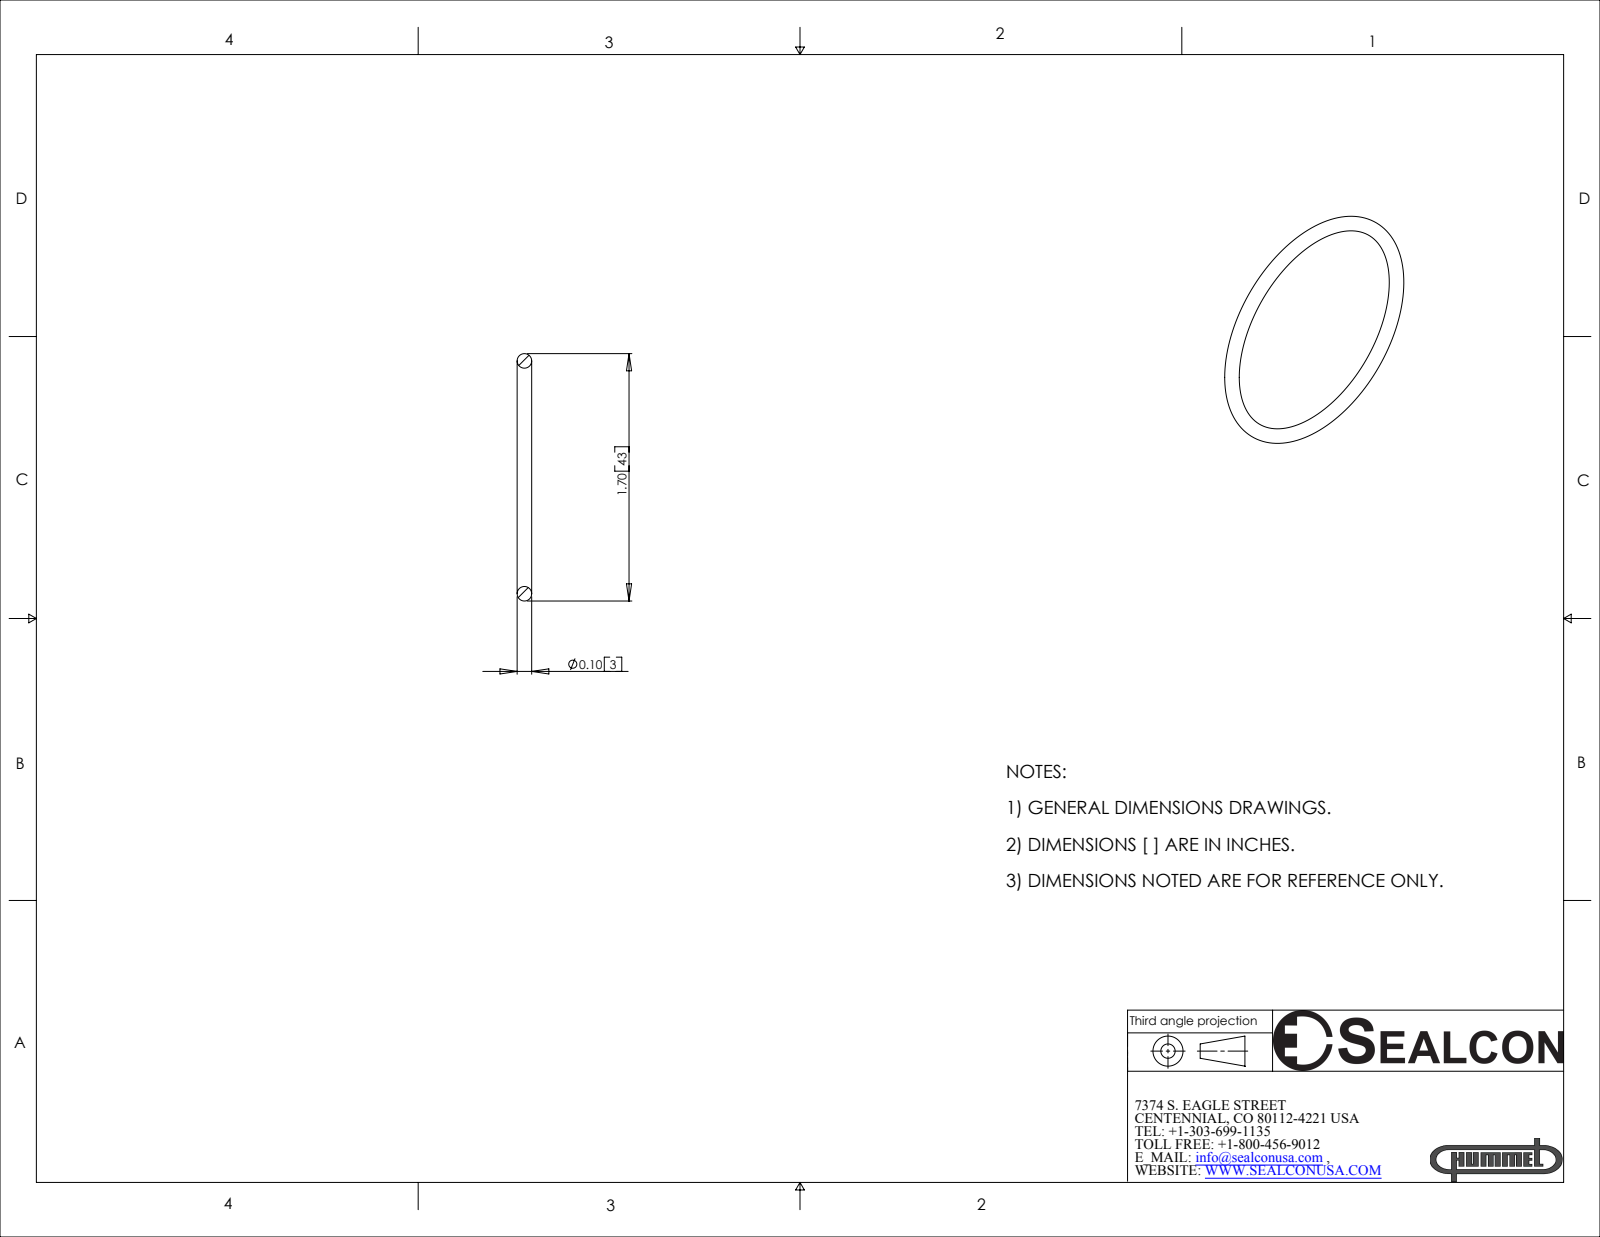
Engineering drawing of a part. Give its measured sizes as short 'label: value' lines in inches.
name: OR-54-VT
written by: SolidWorks 2007 (CONFIG_CONTROL_DESIGN)
unit: in
bodies: 1 solid, 4 faces (0 planar, 0 cylindrical, 4 other)
size: 1.7 × 1.7 × 0.1
volume: 0.039 in³; area: 1.579 in²
